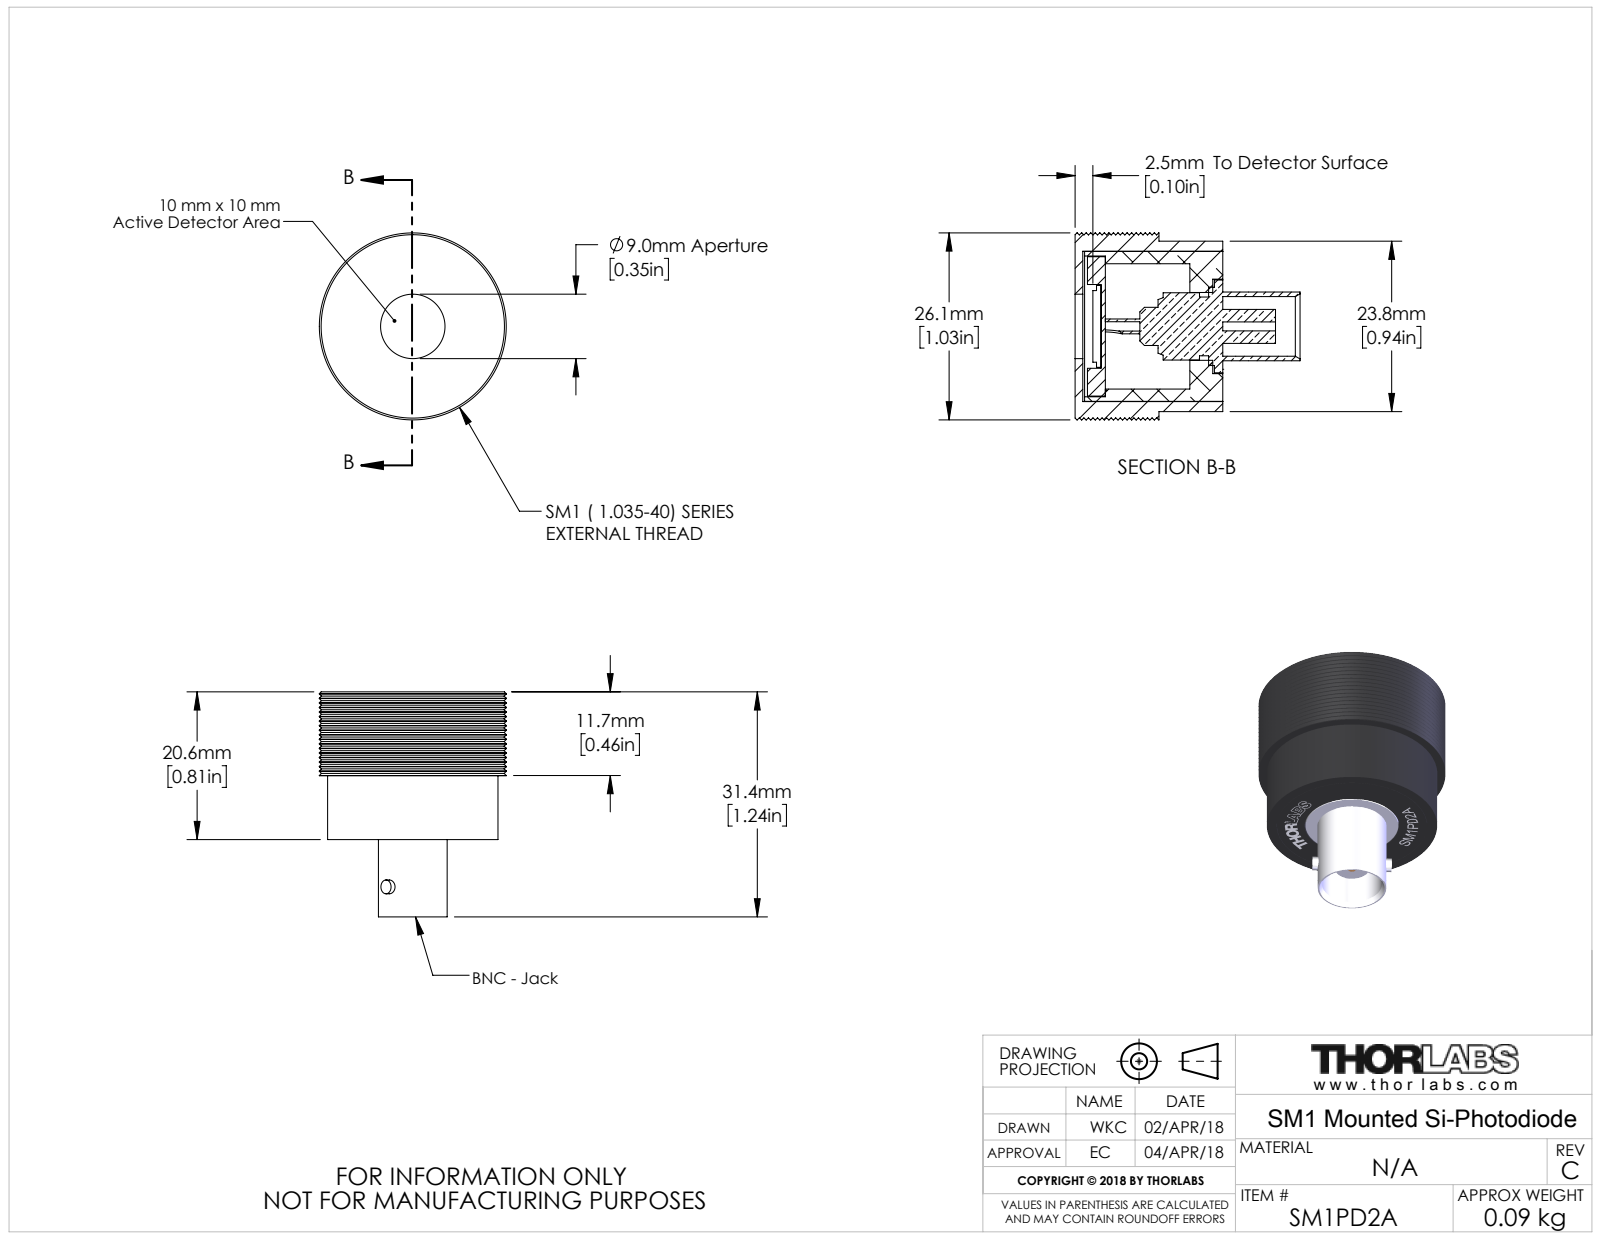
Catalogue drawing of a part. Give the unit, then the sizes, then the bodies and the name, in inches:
Units: inches
Overall size (bounding box): 1.237 × 1.028 × 1.028
Round holes (diameter × count): ⌀0.05 ×1, ⌀0.052 ×1, ⌀0.328 ×1, ⌀0.354 ×1, ⌀0.373 ×1, ⌀0.52 ×1, ⌀0.689 ×1, ⌀0.774 ×1, ⌀0.827 ×1
Round bosses / shafts (diameter × count): ⌀1.028 ×1, ⌀0.937 ×1, ⌀0.824 ×1, ⌀0.766 ×1, ⌀0.51 ×1, ⌀0.43 ×1, ⌀0.378 ×1, ⌀0.37 ×1
Partial cylindrical surfaces — rounded edges, fillets, slot ends (radius × count): R0.039 ×2
Main face-to-face distances: 0.812, 0.646, 0.167, 0.669, 0.024, 0.143, 0.77, 0.124, 0.101, 0.042
Volume: 0.45 in³ · Surface area: 14.78 in²
Bodies: 5 solids, 412 faces (217 planar, 43 cylindrical, 152 other)
Part name (STEP PRODUCT): TTN011350-E0W
STEP written by: SolidWorks 2016 (AUTOMOTIVE_DESIGN)
